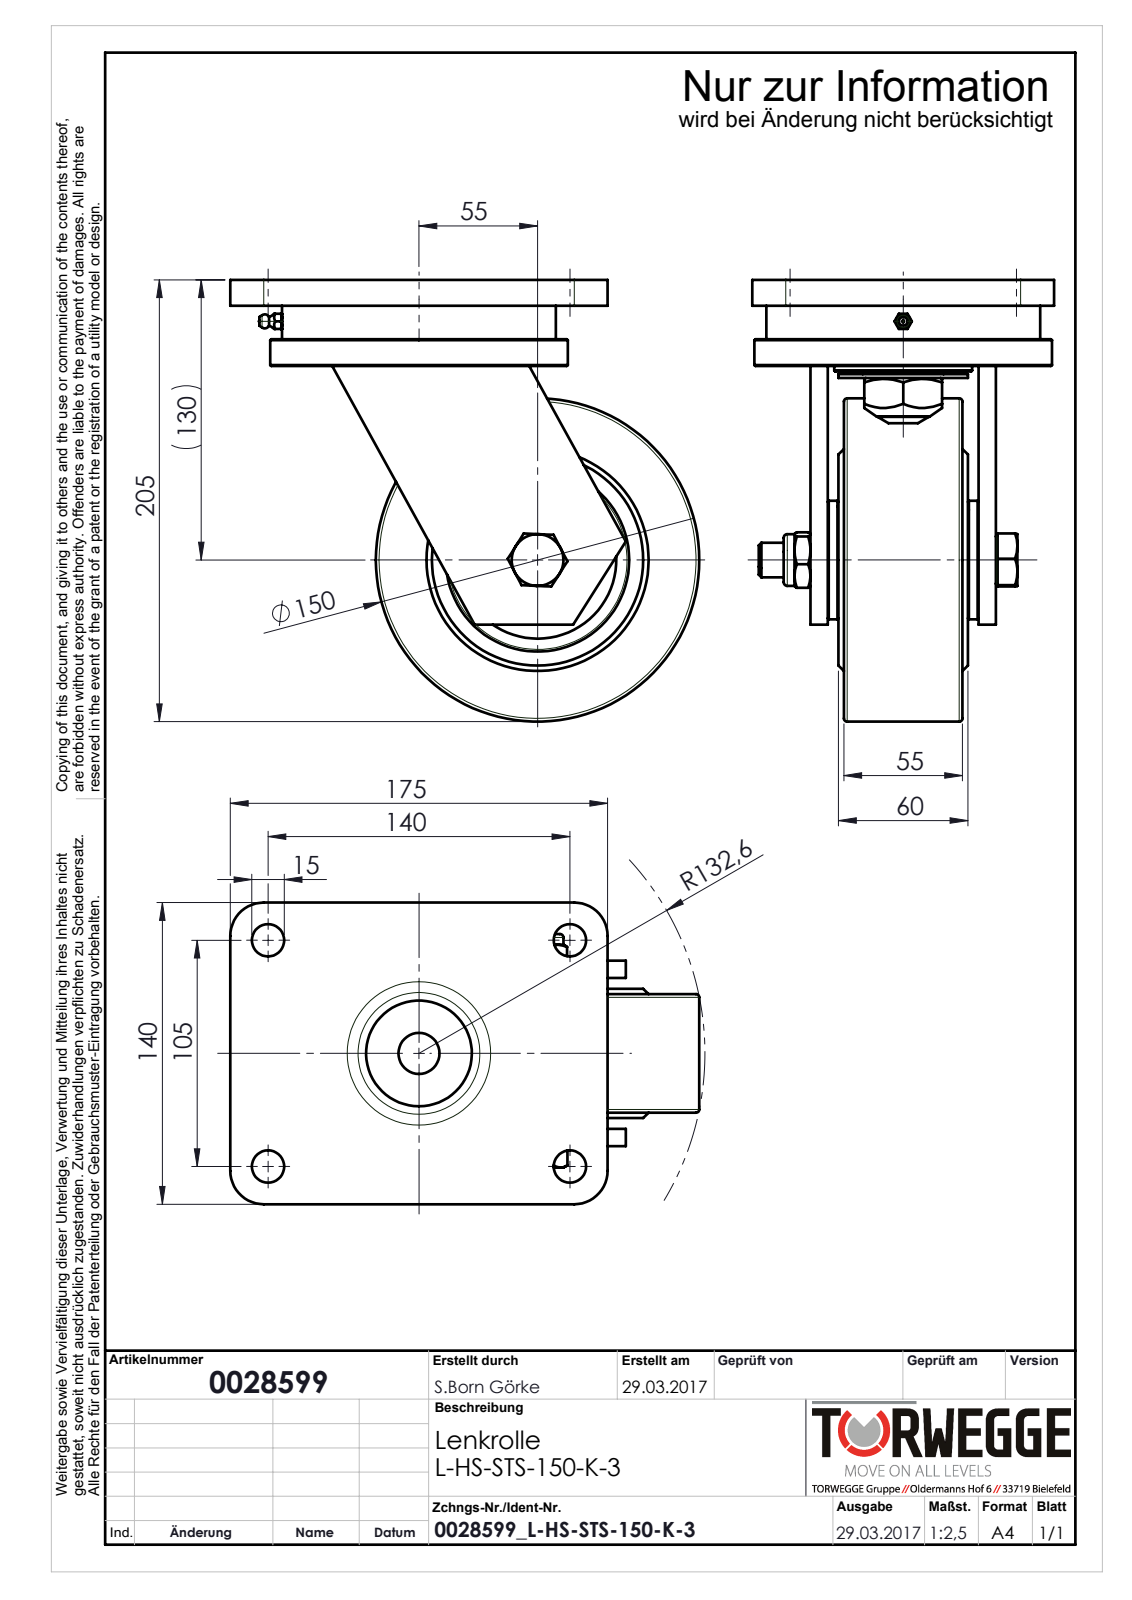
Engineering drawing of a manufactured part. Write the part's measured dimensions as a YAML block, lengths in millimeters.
part_name: "0028599_L-HS-STS-150-K-3"
step_written_by: "SolidWorks 2016 (AUTOMOTIVE_DESIGN)"
units: millimeters
bodies: {solids: 27, faces: 425, planar: 109, cylindrical: 144, other: 172}
overall_size: [217.5, 205, 140]
volume: 1673000
surface_area: 367126
round_holes:
  - {diameter: 15, count: 4}
  - {diameter: 5, count: 1}
  - {diameter: 14, count: 1}
  - {diameter: 16, count: 1}
  - {diameter: 16.5, count: 1}
  - {diameter: 18.29, count: 1}
  - {diameter: 22, count: 1}
  - {diameter: 25, count: 1}
  - {diameter: 30, count: 1}
  - {diameter: 43, count: 1}
  - {diameter: 45, count: 1}
  - {diameter: 48, count: 1}
round_bosses_or_shafts:
  - {diameter: 24, count: 2}
  - {diameter: 150, count: 1}
  - {diameter: 138, count: 1}
  - {diameter: 127, count: 1}
  - {diameter: 119.5, count: 1}
  - {diameter: 118, count: 1}
  - {diameter: 69.5, count: 1}
  - {diameter: 68, count: 1}
partial_cylinders:
  - {radius: 15.5, count: 4}
face_to_face_distances: [15.5, 8, 78, 40, 7.5, 70.5, 62.5, 41, 2.5, 18]
hole_center_spacings: [87.5, 105, 140, 175]
